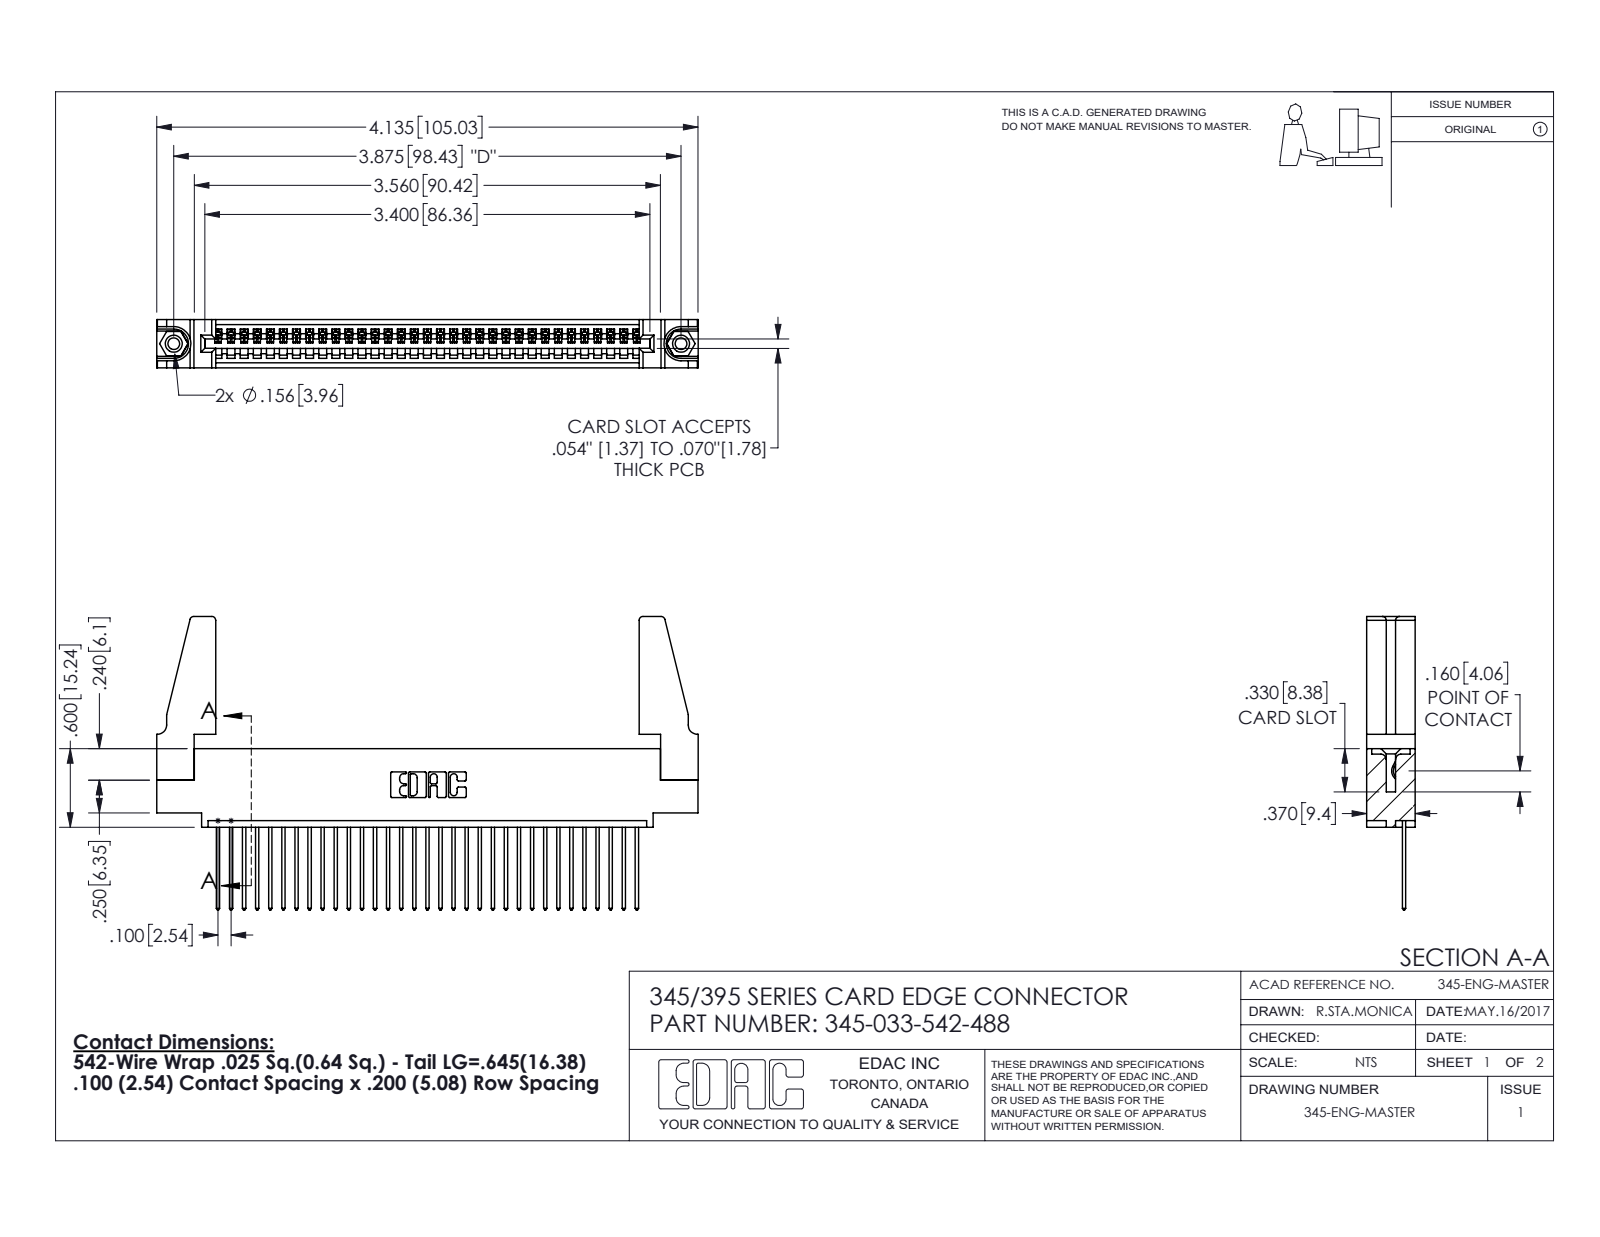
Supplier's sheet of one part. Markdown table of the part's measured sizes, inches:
| quantity | value |
| --- | --- |
| part name | 345-033-542-488; 345-220-078_345-220-088; 345-250-001_345-250-001-102; 345-292-001_345-293-142 (+1 more) |
| STEP written by | SolidWorks 2016 (CONFIG_CONTROL_DESIGN) |
| units | inches |
| bodies | 38 solids, 2168 faces (1476 planar, 676 cylindrical, 16 other) |
| overall size | 4.136 × 2.242 × 0.37 |
| volume | 0.803 in³ |
| surface area | 25.91 in² |
| round holes (diameter × count) | 0.089 × 2, 0.125 × 2, 0.156 × 2, 0.064 × 1 |
| round bosses / shafts (diameter × count) | 0.155 × 2 |
| partial cylindrical surfaces (radius × count) | 0.006 × 66, 0.01 × 66, 0.01 × 22, 0.03 × 8, 0.007 × 6, 0.031 × 6, 0.026 × 3, 0.031 × 2 |
| main face-to-face distances | 0.072, 0.298, 0.37, 0.098, 0.272, 0.025, 0.2, 0.225, 0.149, 0.072 |
| hole center spacings | 0.27, 3.64, 3.875 |
